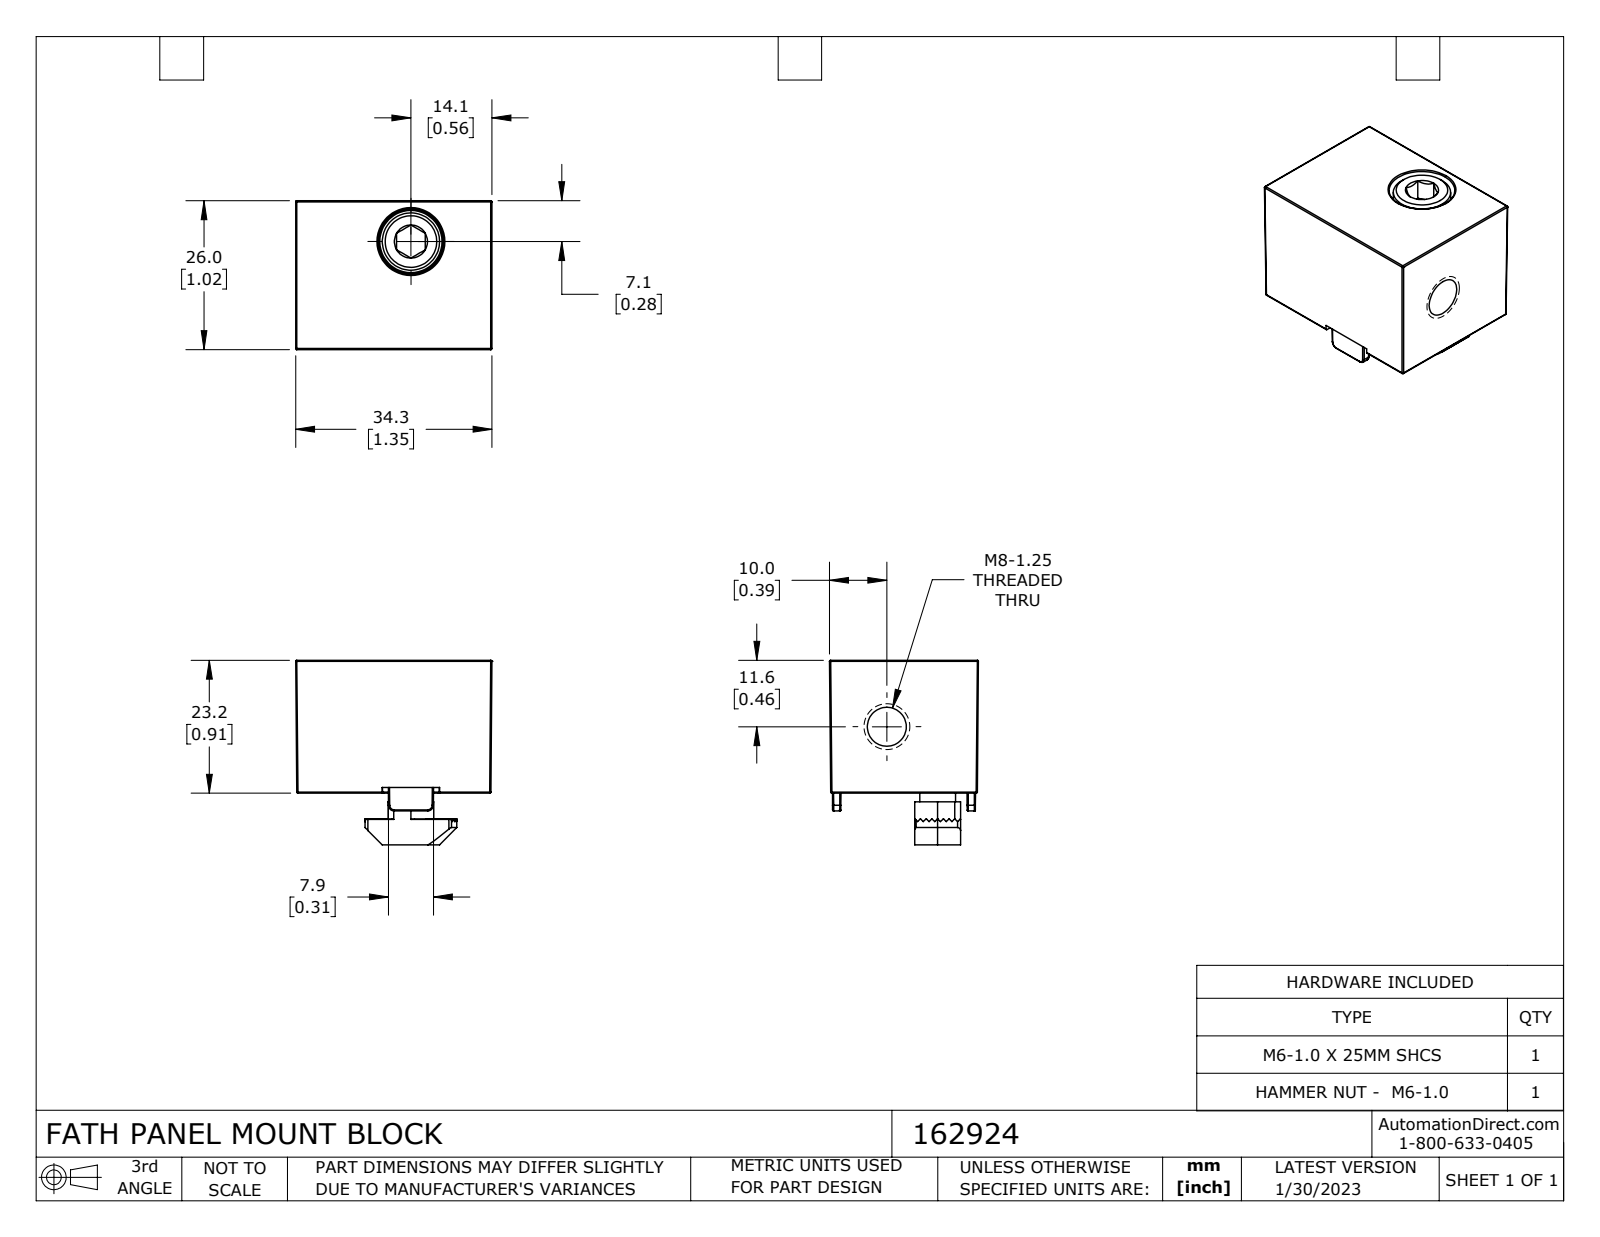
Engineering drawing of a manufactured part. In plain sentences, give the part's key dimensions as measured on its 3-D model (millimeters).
The part is named "162924". Its 3-D file was written by "SolidWorks 2021 (CONFIG_CONTROL_DESIGN)". It is 2 solids with 300 faces: 100 planar, 102 cylindrical and 98 other. Overall it measures 34.3 by 32.2 by 26 millimeters. Its volume is 14 800 cubic millimeters and its surface area 8 787 square millimeters. Round holes: 1 of diameter 5, 1 of diameter 6.8. Round bosses or shafts: 1 of diameter 10, 1 of diameter 6.2. Partial cylindrical surfaces (rounded edges, fillets, slot ends): 34 of radius 0.2, 19 of radius 0.5, 7 of radius 0.1, 4 of radius 1, 1 of radius 4, 1 of radius 5.4, 1 of radius 8. The main face-to-face distances are 23.2, 23.1, 17.1, 8, 15.1, 8.1, 3, 9.4, 9, 23.8.
